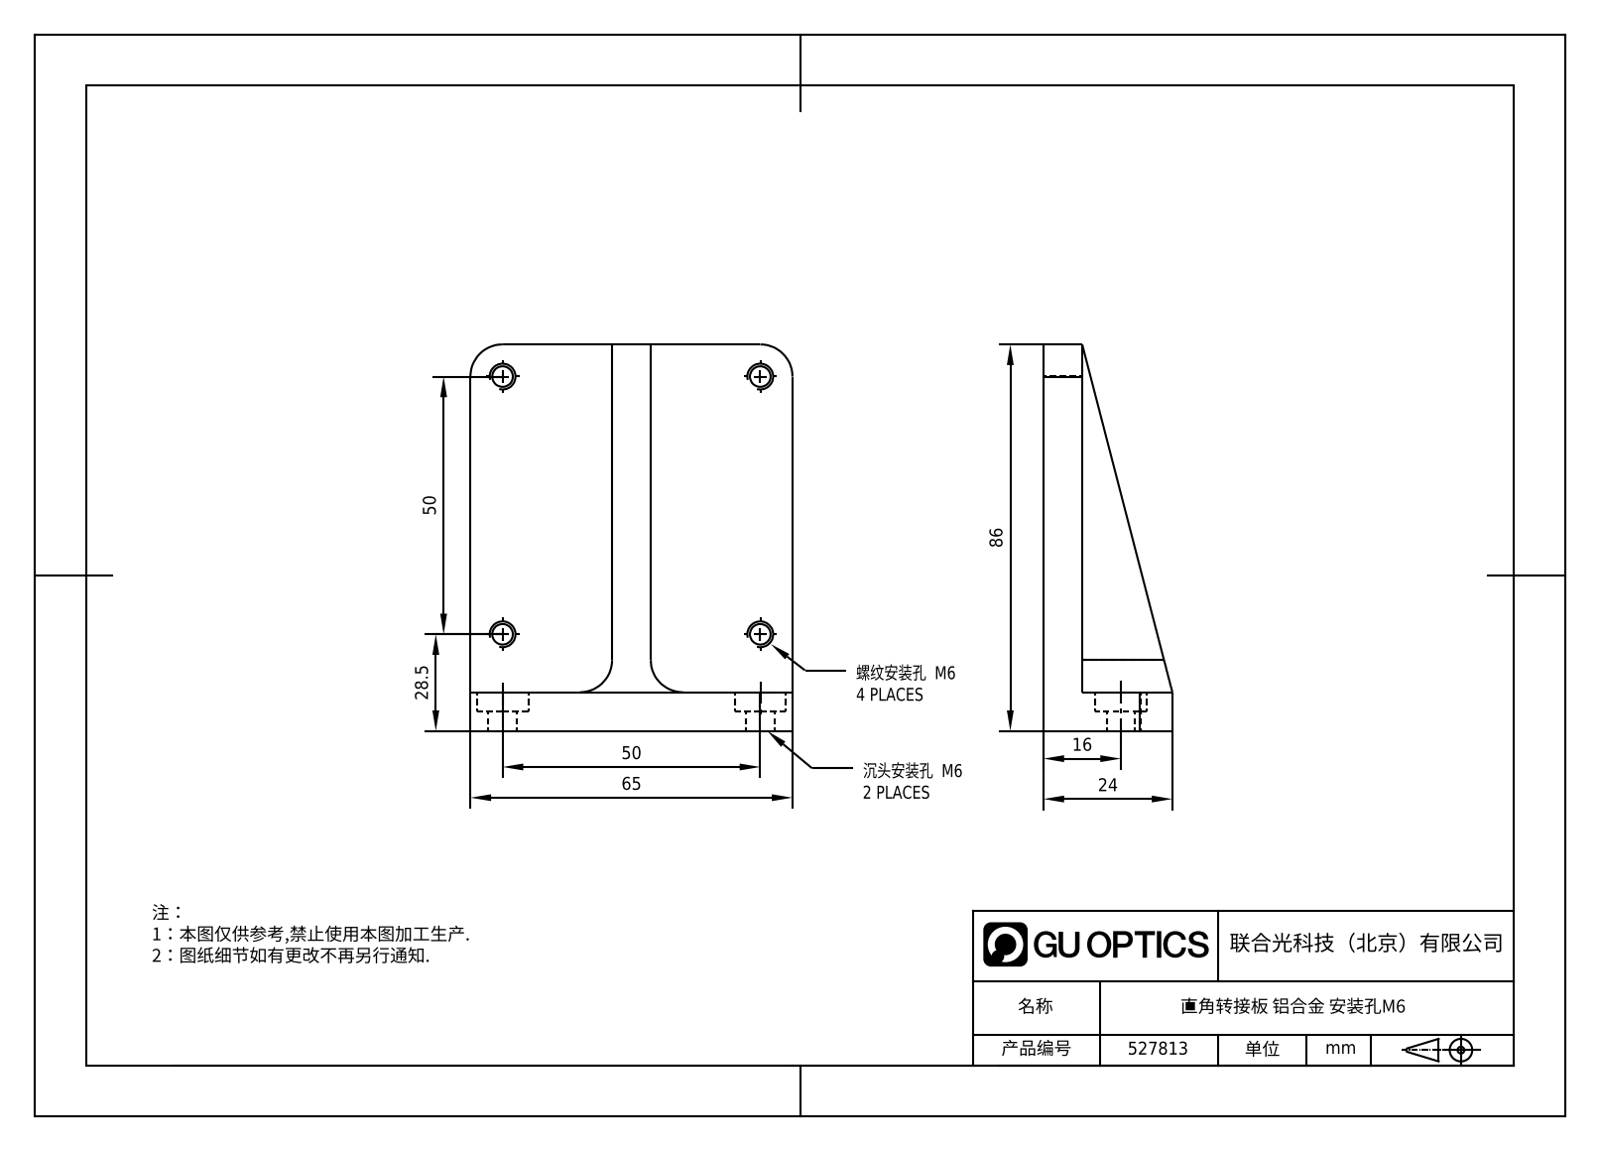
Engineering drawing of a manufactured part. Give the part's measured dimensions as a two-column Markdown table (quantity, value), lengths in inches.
| quantity | value |
| --- | --- |
| part name | 1.6.9.5_ZSJ-Z065_65mm直角转接板，带M6螺孔和M6沉头孔 |
| STEP written by | SolidWorks 2021 (CONFIG_CONTROL_DESIGN) |
| units | inches |
| bodies | 1 solid, 37 faces (15 planar, 22 cylindrical, 0 other) |
| overall size | 3.386 × 2.559 × 0.945 |
| volume | 2.781 in³ |
| surface area | 26.63 in² |
| round holes (diameter × count) | 0.197 × 4, 0.256 × 2, 0.433 × 2 |
| partial cylindrical surfaces (radius × count) | 0.295 × 6 |
| main face-to-face distances | 0.236, 1.161, 1.398, 0.315, 2.559, 0.945, 0.709, 3.386, 3.071, 0.118 |
| hole center spacings | 1.969, 2.784 |
